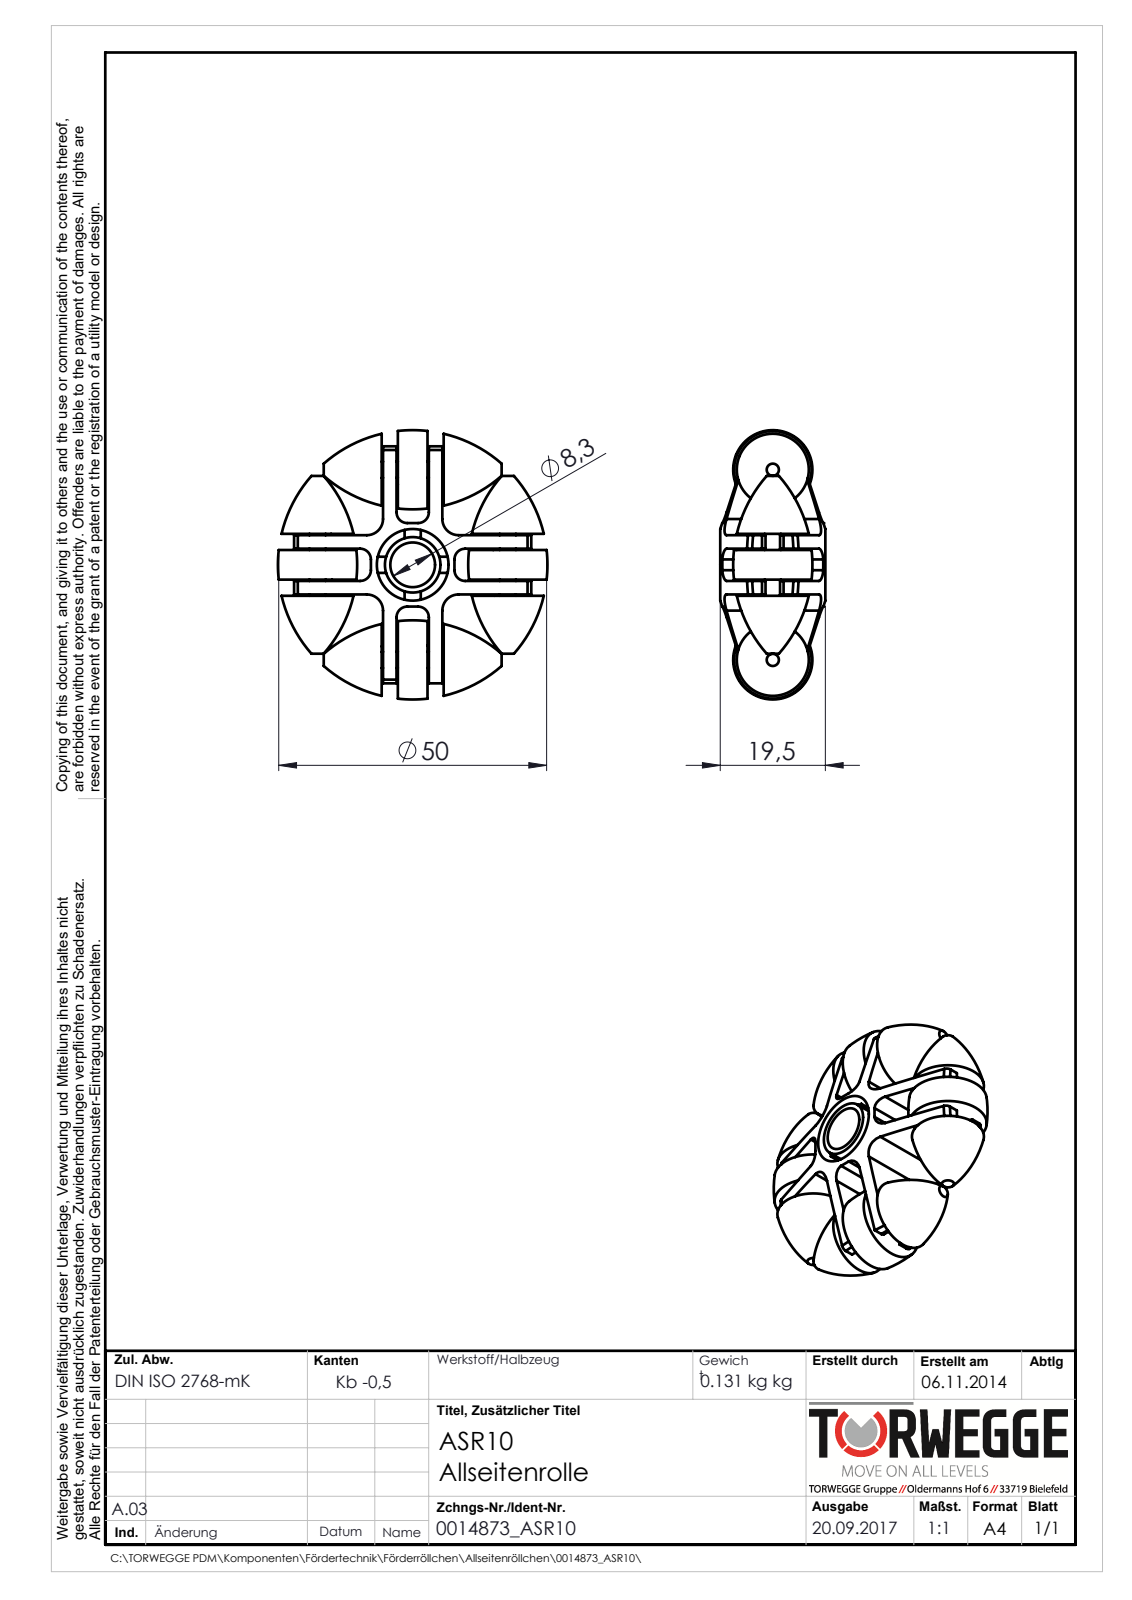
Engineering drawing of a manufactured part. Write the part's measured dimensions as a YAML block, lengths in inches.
part_name: "0014873_ASR10; ASR10_Halter; ASR10_Roellchen; ASR10_Achse"
step_written_by: "SolidWorks 2016 (AUTOMOTIVE_DESIGN)"
units: inches
bodies: {solids: 17, faces: 231, planar: 111, cylindrical: 61, other: 59}
overall_size: [1.969, 1.969, 0.768]
volume: 1.009
surface_area: 20.92
round_holes:
  - {diameter: 0.118, count: 4}
  - {diameter: 0.122, count: 4}
  - {diameter: 0.327, count: 1}
  - {diameter: 0.374, count: 1}
  - {diameter: 0.524, count: 1}
round_bosses_or_shafts:
  - {diameter: 0.406, count: 1}
partial_cylinders:
  - {radius: 0.079, count: 8}
  - {radius: 0.118, count: 4}
  - {radius: 0.039, count: 1}
face_to_face_distances: [0.108, 0.335, 0.325, 0.226, 0.098, 0.118, 0.344, 0.443, 0.433, 0.217]
hole_center_spacings: [1.39]
